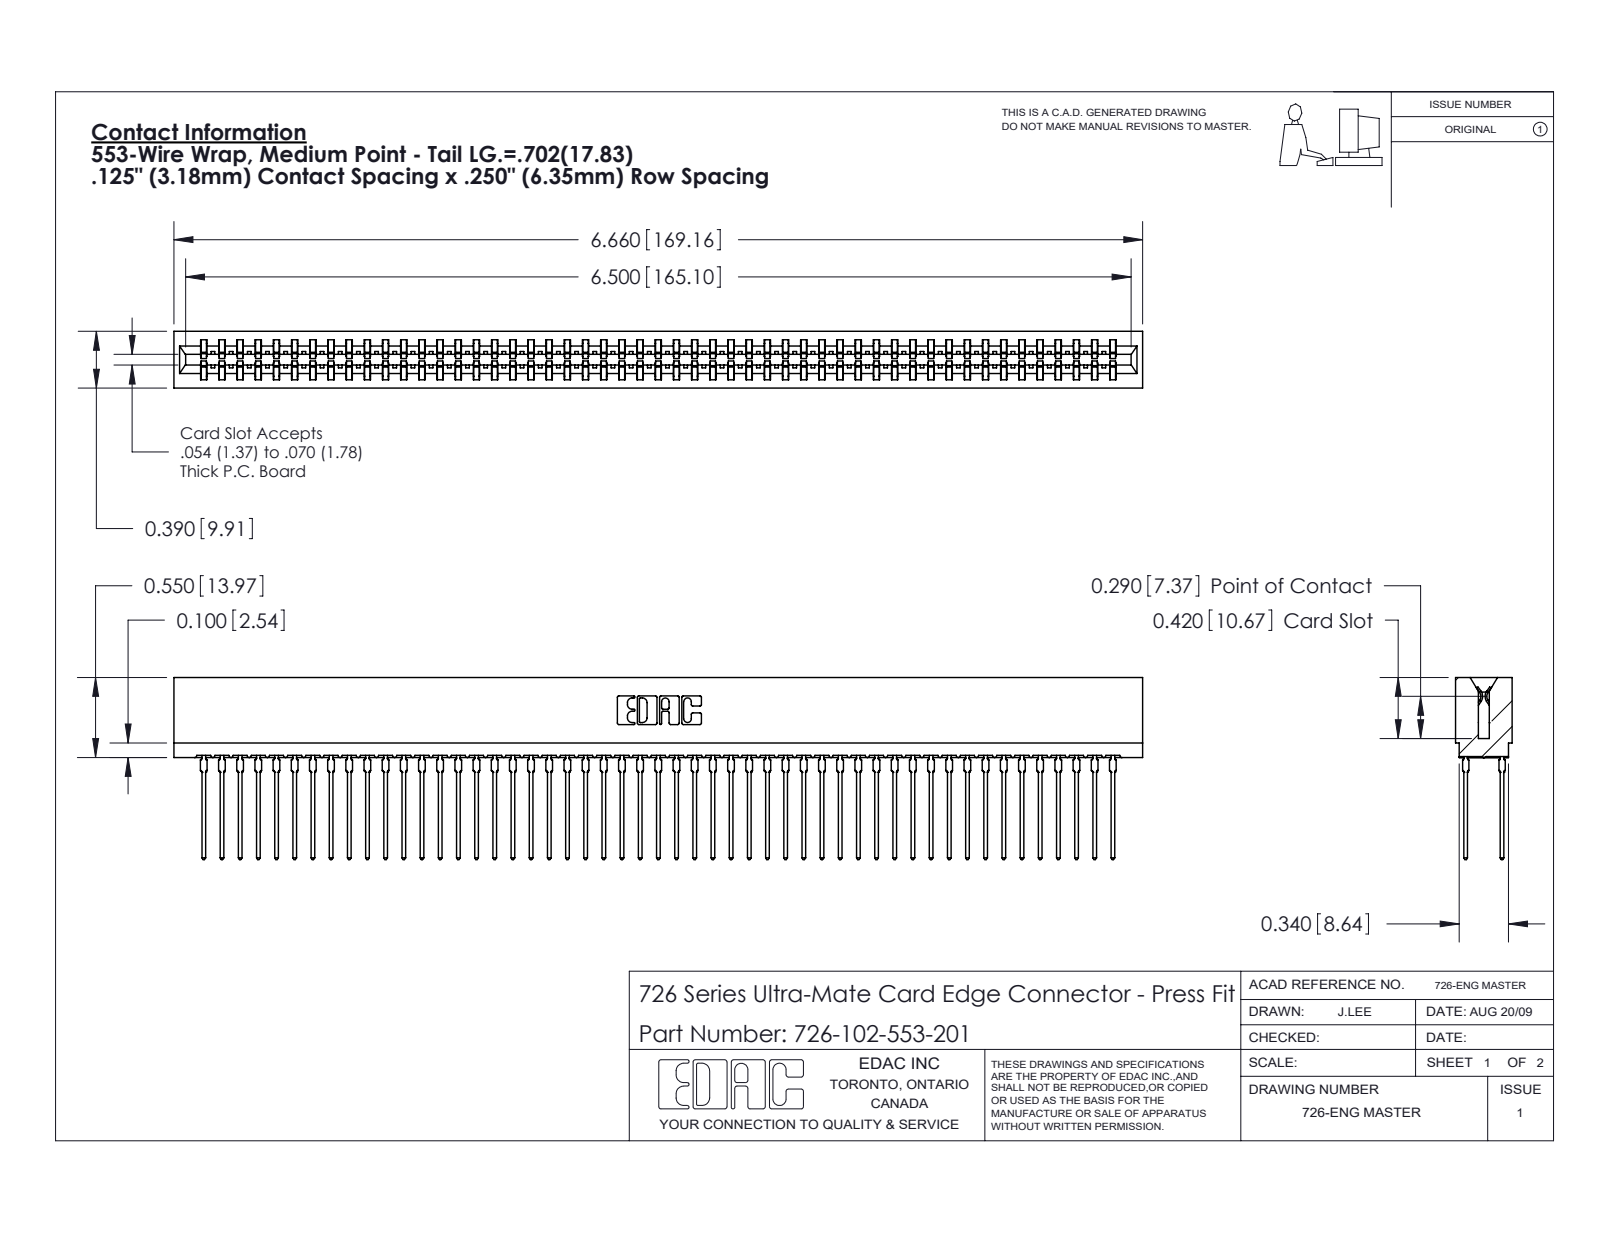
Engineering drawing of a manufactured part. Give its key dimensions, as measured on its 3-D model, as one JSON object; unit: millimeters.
{"part_name": "746-292-001_553; 726 Part_.515 Slot Depth - 01; 726-102-553-201", "step_written_by": "SolidWorks 2020 (CONFIG_CONTROL_DESIGN)", "units": "millimeters", "bodies": {"solids": 103, "faces": 9226, "planar": 4747, "cylindrical": 1827, "other": 2652}, "overall_size": [169.2, 31.8, 9.9], "volume_mm3": 16000, "surface_area_mm2": 28850, "partial_cylinders_radius": [[0.5, 204], [0.4, 52], [0.3, 22], [0.1, 8], [0.3, 8], [0.2, 6], [0.8, 6], [0.7, 3]], "face_to_face_distances": [1.4, 8.5, 0.6, 7.8, 6.4, 9.9, 2.1, 7, 5.7, 9.3]}
